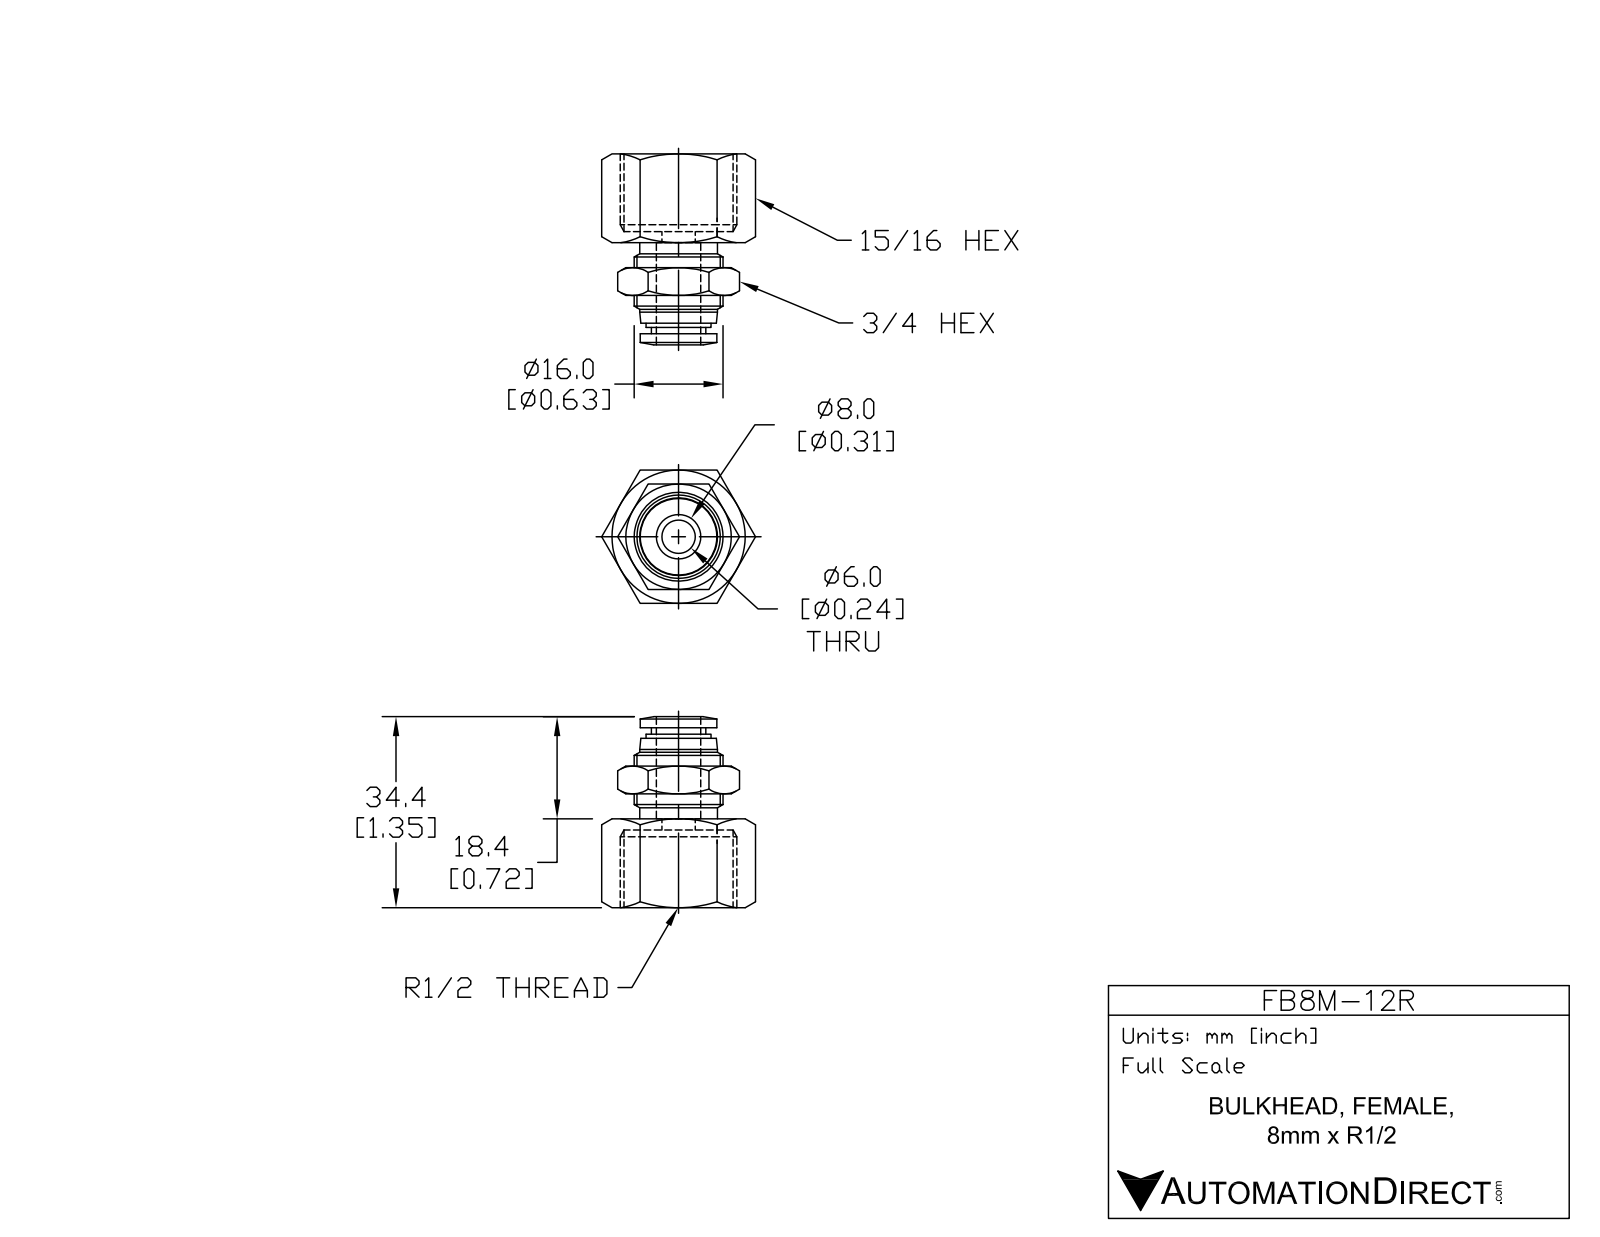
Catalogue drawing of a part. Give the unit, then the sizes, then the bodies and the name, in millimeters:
Units: millimetres
Overall size (bounding box): 34.4 × 27.7 × 24
Round holes (diameter × count): ⌀6 ×1, ⌀8.3 ×1
Round bosses / shafts (diameter × count): ⌀16 ×1, ⌀14 ×1, ⌀13.8 ×1, ⌀11.7 ×1, ⌀9.8 ×1
Main face-to-face distances: 24, 2, 2.5, 21.5, 19, 14, 16, 25.2, 11.2, 9.2
Volume: 5 930 mm³ · Surface area: 4 909 mm²
Bodies: 1 solid, 80 faces (22 planar, 18 cylindrical, 40 other)
Part name (STEP PRODUCT): FB8M-12R
STEP written by: SolidWorks 2015 (AUTOMOTIVE_DESIGN)
